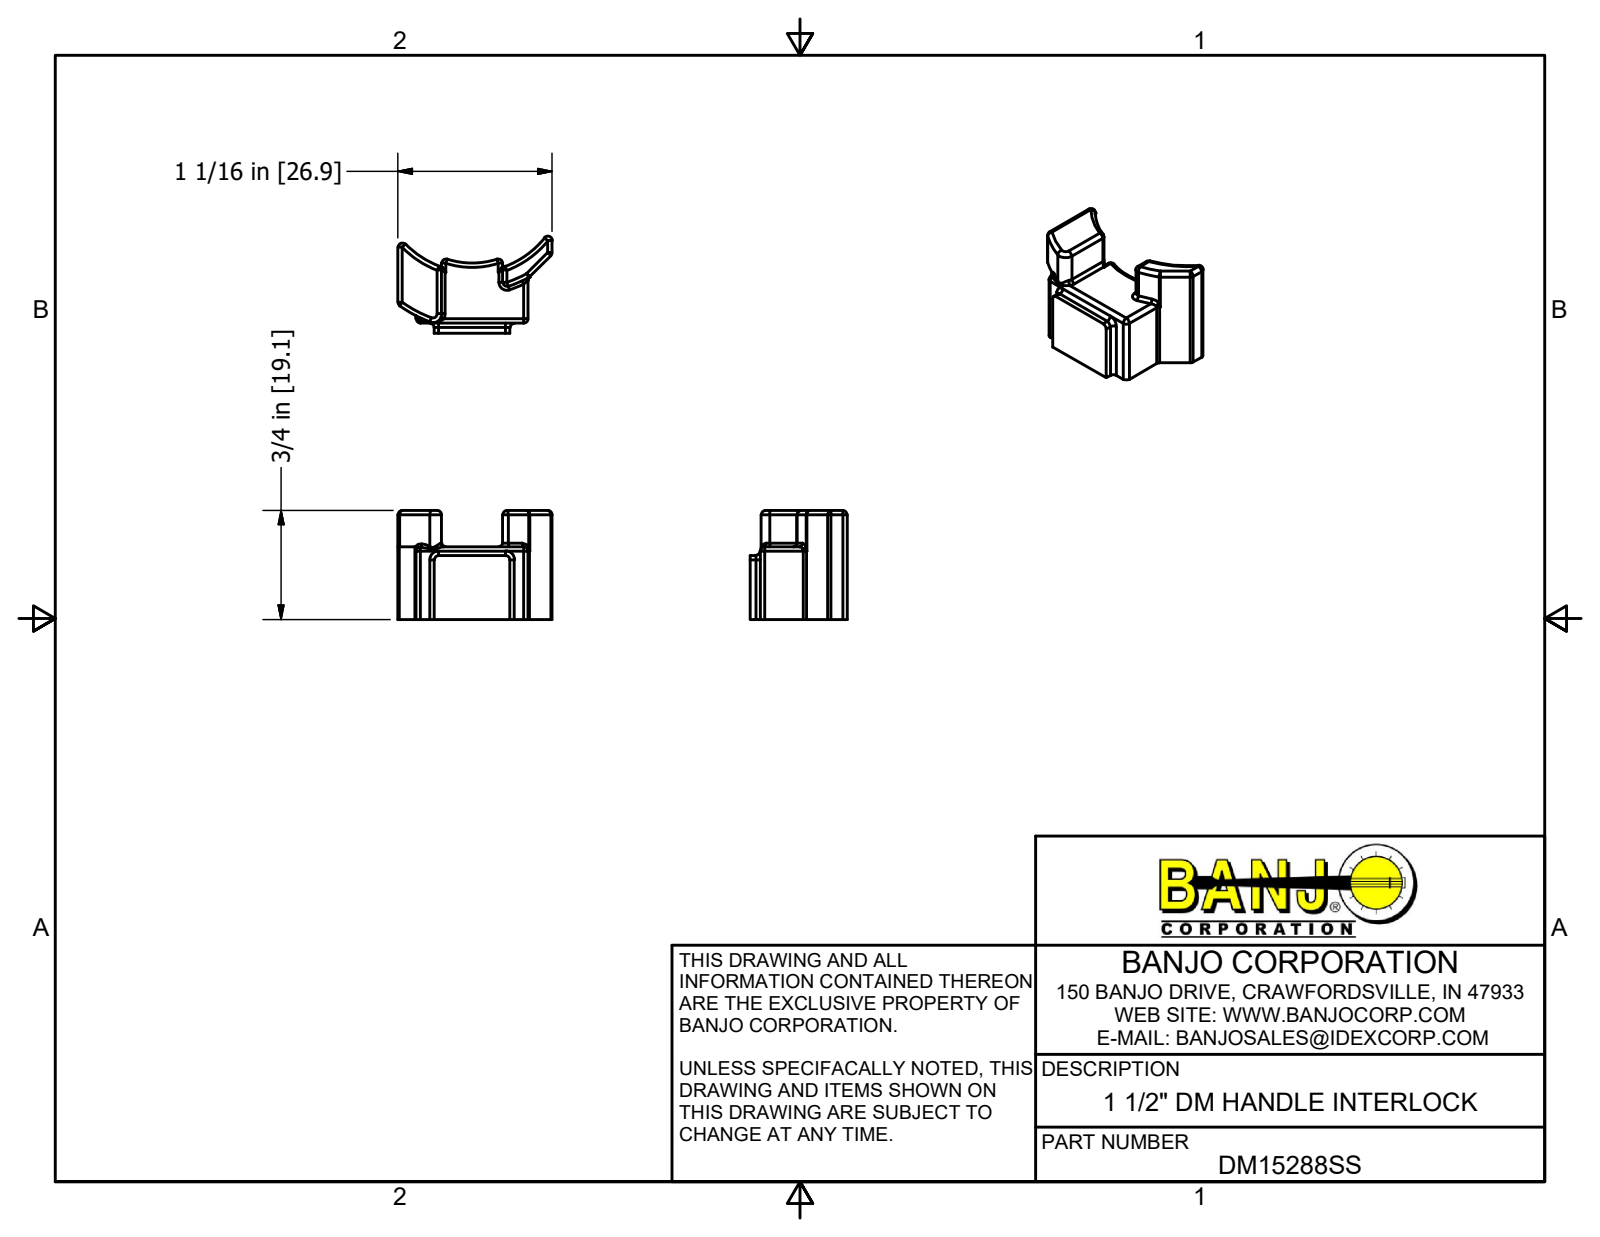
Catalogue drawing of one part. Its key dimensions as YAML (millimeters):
part_name: "DM15288SS; DM15288SSX"
step_written_by: "Autodesk Inventor 2017 (AUTOMOTIVE_DESIGN)"
units: millimeters
bodies: {solids: 1, faces: 120, planar: 23, cylindrical: 45, other: 52}
overall_size: [26.92, 19.05, 16.95]
volume: 3400
surface_area: 2217
partial_cylinders:
  - {radius: 0.76, count: 31}
  - {radius: 0.64, count: 4}
  - {radius: 1.59, count: 2}
  - {radius: 3.43, count: 2}
  - {radius: 1.52, count: 1}
  - {radius: 14.22, count: 1}
  - {radius: 16.26, count: 1}
  - {radius: 20.32, count: 1}
face_to_face_distances: [12.7, 6.35, 22.73, 3.17, 19.56, 19.05, 3.18, 4.45, 15.11, 4.96]
